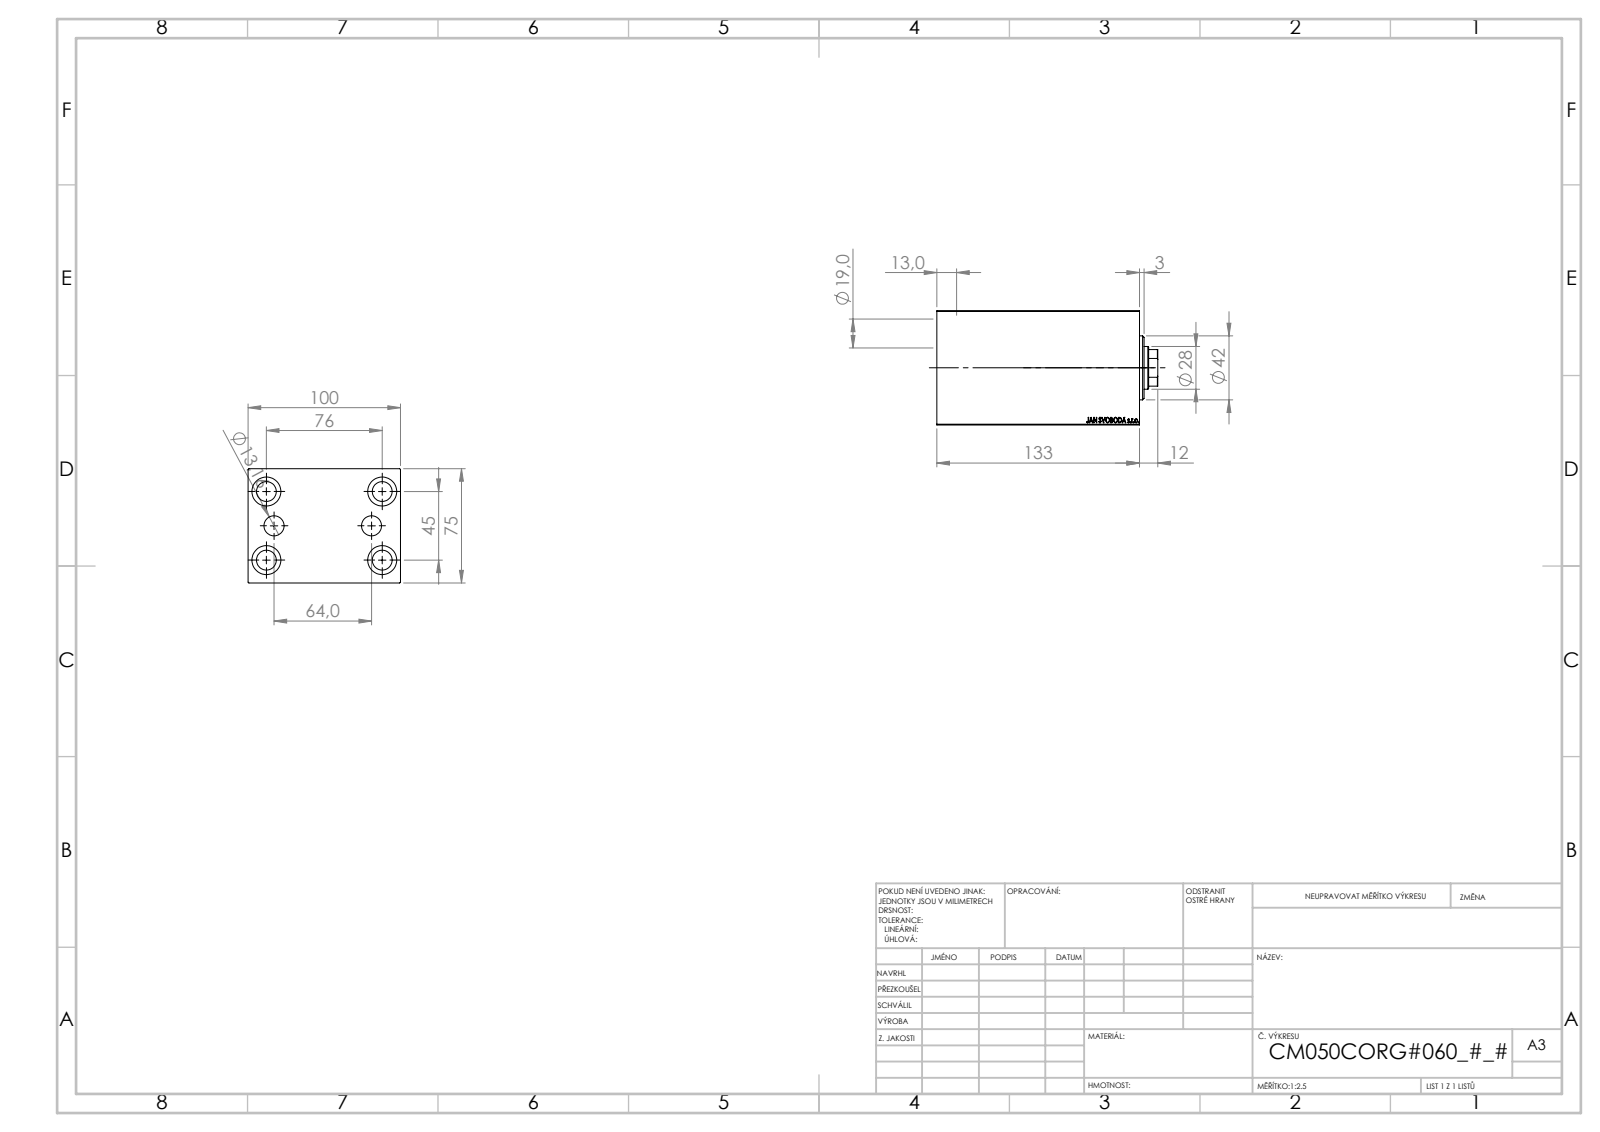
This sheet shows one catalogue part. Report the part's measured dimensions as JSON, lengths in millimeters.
{"part_name": "V450CM_C_VCP; V450CM_C_Body; V450CM_VC_B", "step_written_by": "SolidWorks 2019 (CONFIG_CONTROL_DESIGN)", "units": "millimeters", "bodies": {"solids": 3, "faces": 855, "planar": 407, "cylindrical": 54, "other": 394}, "overall_size": [145, 100, 75], "volume_mm3": 829034, "surface_area_mm2": 131427, "round_holes": [[13, 4], [19, 4], [13.16, 2], [18.5, 1], [28, 1], [31.5, 1], [50, 1], [52, 1], [57, 1]], "round_bosses_or_shafts": [[42, 1]], "partial_cylinders_radius": [[13.5, 1]], "face_to_face_distances": [75, 100, 133, 119, 14, 107, 12, 121, 72, 60], "hole_center_spacings": [44.16, 23.05, 23.56, 45, 72.58, 74.48, 76, 88.32]}
